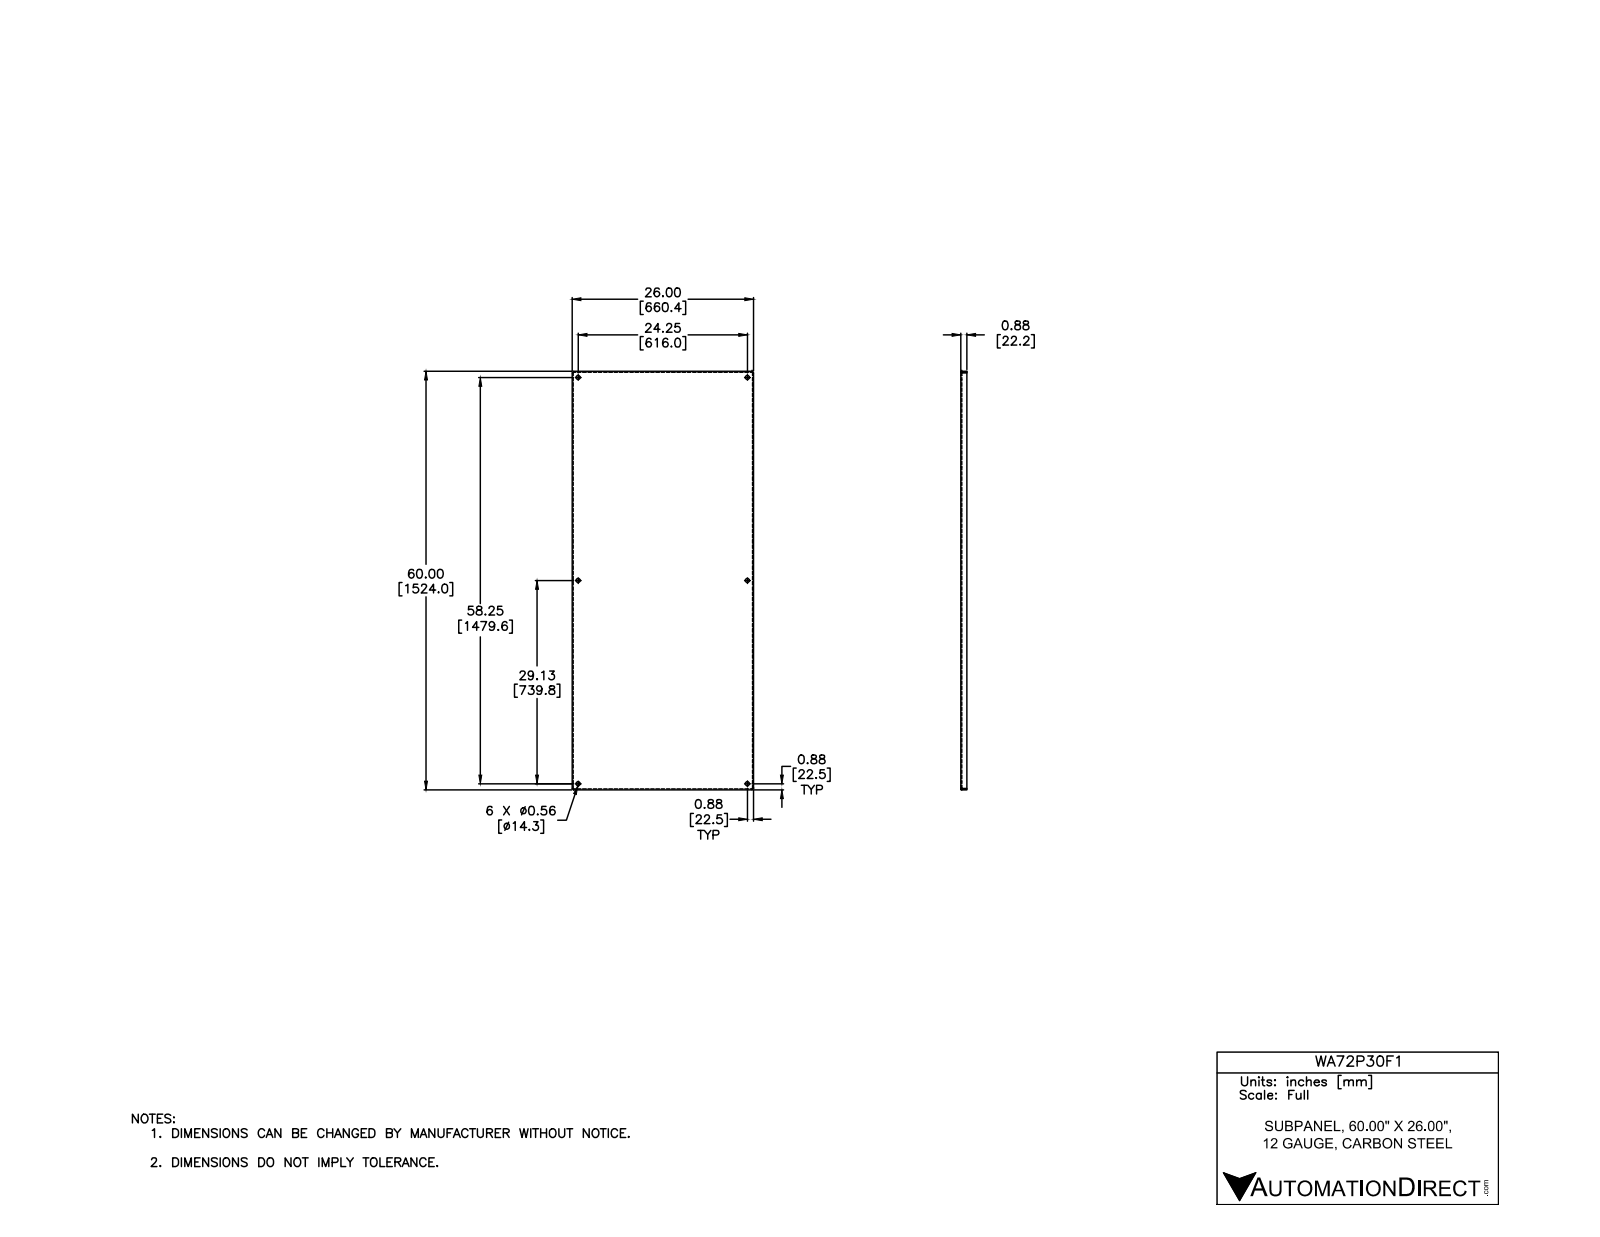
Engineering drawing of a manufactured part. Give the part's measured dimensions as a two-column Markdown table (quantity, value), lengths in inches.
| quantity | value |
| --- | --- |
| part name | WA_P_F |
| STEP written by | Autodesk Inventor 2012 (AUTOMOTIVE_DESIGN) |
| units | inches |
| bodies | 1 solid, 44 faces (22 planar, 14 cylindrical, 8 other) |
| overall size | 60 × 26 × 0.875 |
| volume | 158.1 in³ |
| surface area | 3 390 in² |
| round holes (diameter × count) | 0.563 × 6 |
| partial cylindrical surfaces (radius × count) | 0.031 × 4, 0.125 × 4 |
| main face-to-face distances | 0.094, 25.906, 26, 25.813, 59.906, 60, 59.813, 0.781, 0.875, 0.16 |
| hole center spacings | 29.125, 37.899, 24.25, 24.25, 29.125, 37.899, 58.25, 58.25 |
